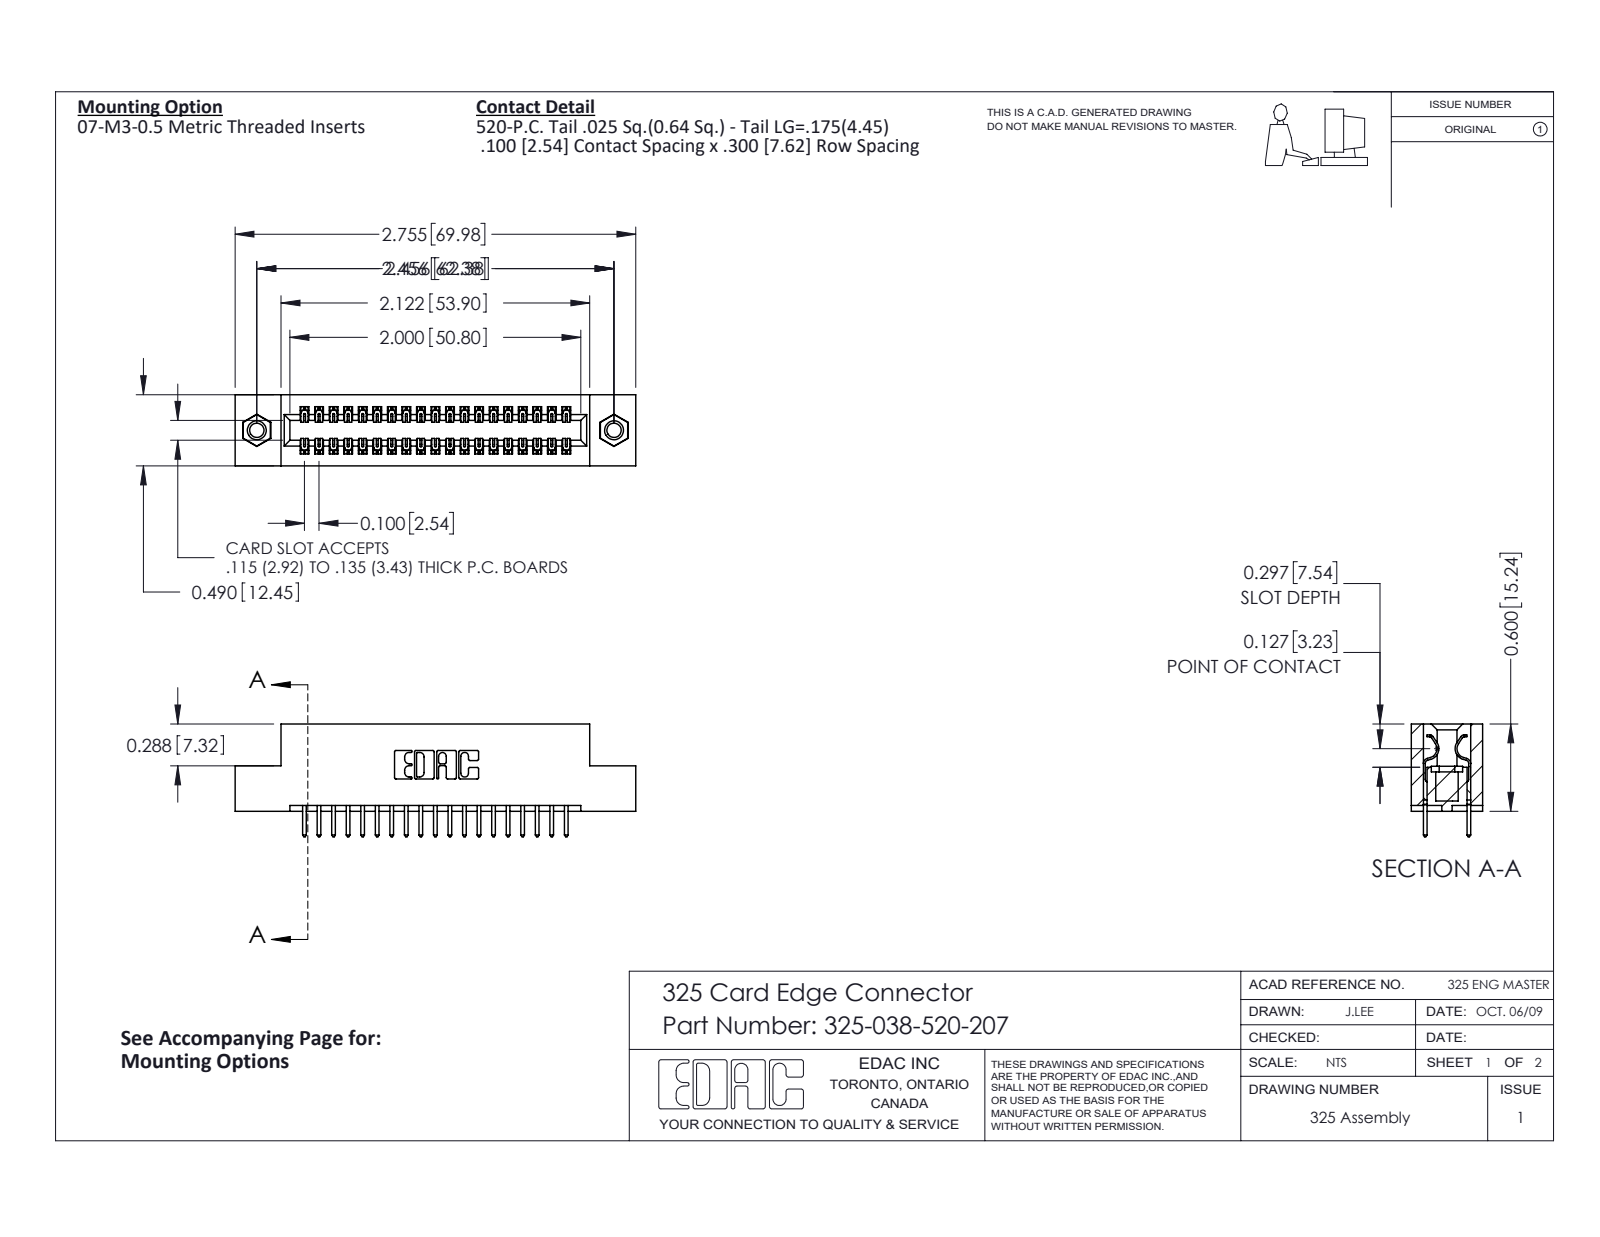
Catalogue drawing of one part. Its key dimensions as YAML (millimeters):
part_name: "345-250-001_345-250-005-103; 325-038-520-207; 325 Part_TI; 325-292-001_325-293-120"
step_written_by: "SolidWorks 2016 (CONFIG_CONTROL_DESIGN)"
units: millimeters
bodies: {solids: 41, faces: 2150, planar: 1470, cylindrical: 664, other: 16}
overall_size: [70, 19.7, 12.4]
volume: 8820
surface_area: 10060
round_holes:
  - {diameter: 2.5, count: 2}
  - {diameter: 3.2, count: 2}
  - {diameter: 4.1, count: 2}
round_bosses_or_shafts:
  - {diameter: 3.9, count: 2}
partial_cylinders:
  - {radius: 0.2, count: 57}
  - {radius: 0.3, count: 38}
  - {radius: 0.3, count: 22}
  - {radius: 0.2, count: 6}
  - {radius: 0.8, count: 6}
  - {radius: 0.7, count: 3}
  - {radius: 0.4, count: 2}
  - {radius: 0.6, count: 2}
face_to_face_distances: [2.1, 10.3, 7.6, 12.4, 2.7, 9.7, 0.6, 8.3, 1, 2.5]
hole_center_spacings: [62.4]
